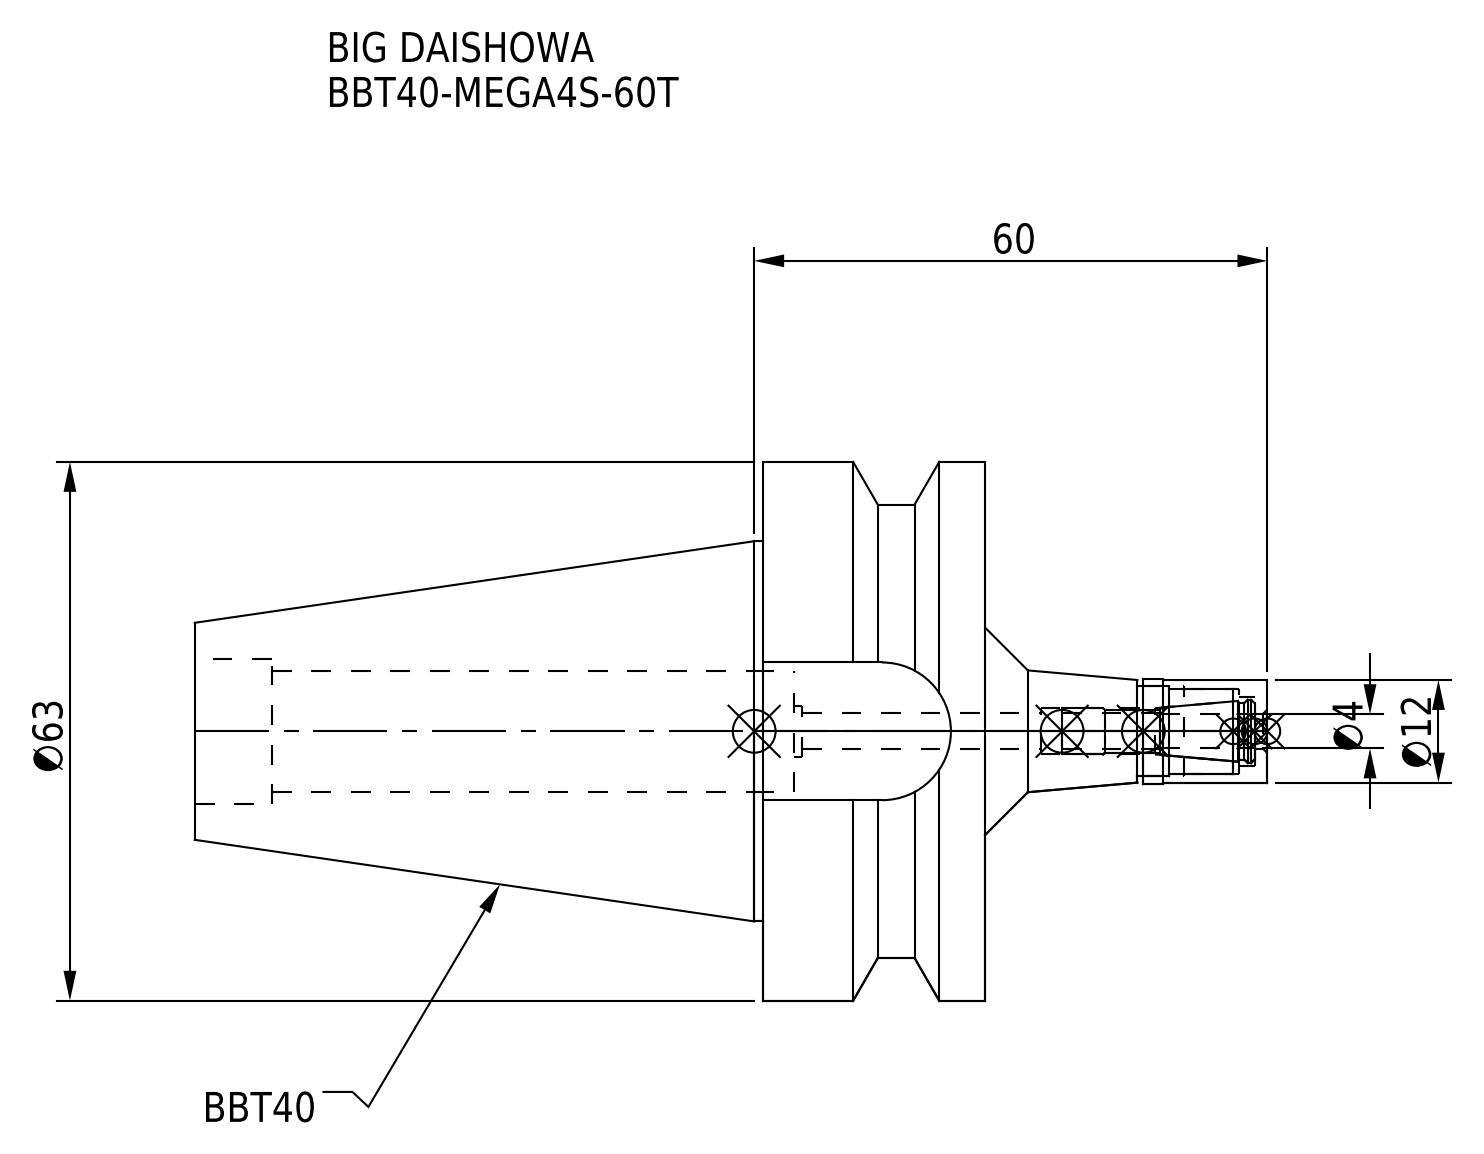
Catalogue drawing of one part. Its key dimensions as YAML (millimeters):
part_name: "BBT40-MEGA4S-60T_1.stp; BBT40-MEGA4S-60T-040.stp; MGN4S_1.stp; DXF_TEMP_ASSY_ASM_4_ASM.stp (+3 more)"
step_written_by: "SolidWorks 2019 (CONFIG_CONTROL_DESIGN)"
units: millimeters
bodies: {solids: 2, faces: 74, planar: 22, cylindrical: 38, other: 14}
overall_size: [125.4, 63, 63]
volume: 127631
surface_area: 24910
round_holes:
  - {diameter: 4.1, count: 1}
  - {diameter: 4.2, count: 1}
  - {diameter: 5.4, count: 1}
  - {diameter: 6, count: 1}
  - {diameter: 8, count: 1}
  - {diameter: 10, count: 1}
  - {diameter: 10.5, count: 1}
  - {diameter: 14.2, count: 1}
  - {diameter: 17, count: 1}
round_bosses_or_shafts:
  - {diameter: 63, count: 1}
  - {diameter: 53, count: 1}
  - {diameter: 44.45, count: 1}
  - {diameter: 12.3, count: 1}
  - {diameter: 12, count: 1}
partial_cylinders:
  - {radius: 8.05, count: 1}
face_to_face_distances: [26, 45, 92.4, 66.4, 16.1, 22.4, 3.6, 70, 33, 55.4]
